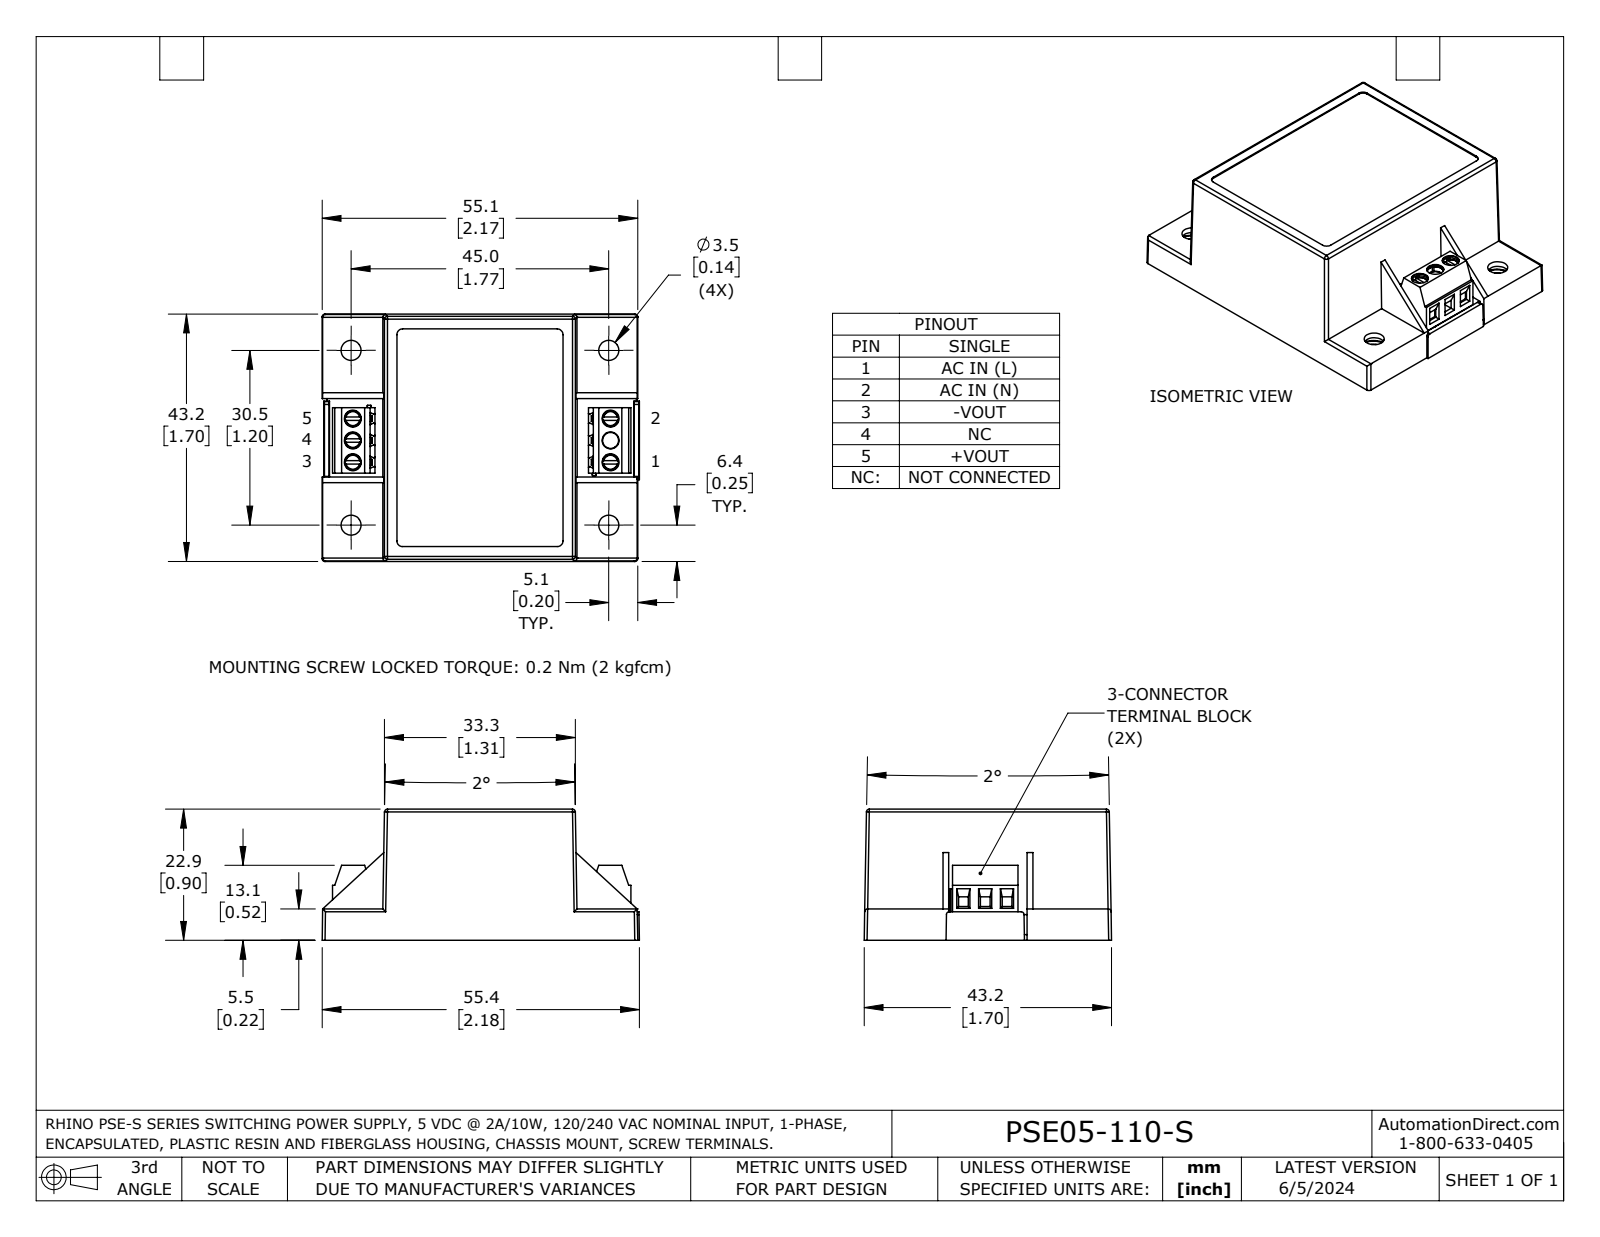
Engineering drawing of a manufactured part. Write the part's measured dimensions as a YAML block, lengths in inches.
part_name: "PSE05-110-S"
step_written_by: "SolidWorks 2023 (AUTOMOTIVE_DESIGN)"
units: inches
bodies: {solids: 1, faces: 488, planar: 328, cylindrical: 123, other: 37}
overall_size: [2.181, 1.701, 0.902]
volume: 0.521
surface_area: 27.5
round_holes:
  - {diameter: 0.138, count: 8}
  - {diameter: 0.116, count: 6}
  - {diameter: 0.11, count: 1}
partial_cylinders:
  - {radius: 0.009, count: 18}
  - {radius: 0.02, count: 18}
  - {radius: 0.006, count: 12}
  - {radius: 0.004, count: 8}
  - {radius: 0.01, count: 4}
  - {radius: 0.039, count: 4}
  - {radius: 0.079, count: 4}
  - {radius: 0.012, count: 2}
face_to_face_distances: [0.039, 0.854, 0.177, 0.677, 0.815, 0.894, 0.138, 0.717, 1.622, 1.264]
hole_center_spacings: [1.772, 2.14, 0.022, 0.15, 0.45, 0.6, 0.75, 1.201]
